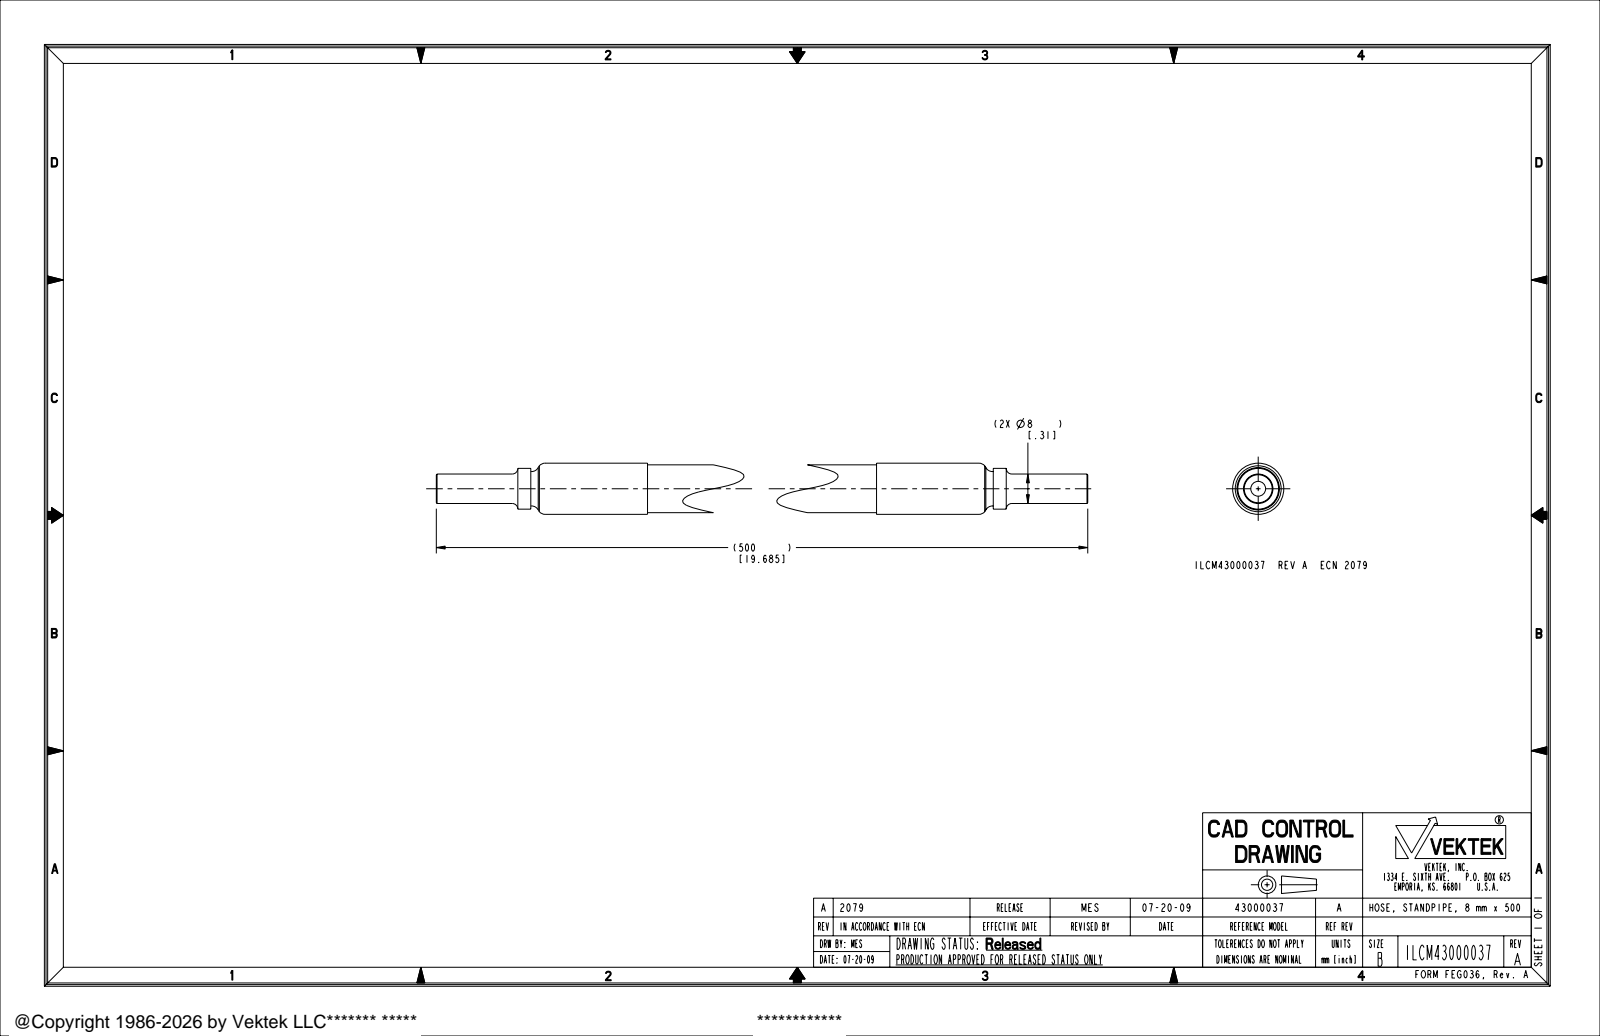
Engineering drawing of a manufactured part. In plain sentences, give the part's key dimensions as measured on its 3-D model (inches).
The part is named "ILCM43000037". Its 3-D file was written by "PRO/ENGINEER BY PARAMETRIC TECHNOLOGY CORPORATION, 2007460 (AUTOMOTIVE_DESIGN_CC2)". It is 1 solid with 74 faces: 14 planar, 28 cylindrical and 32 other. Overall it measures 19.685 by 0.543 by 0.543 inches. Its volume is 3.035 cubic inches and its surface area 51.88 square inches. Round holes: 1 of diameter 0.157, 1 of diameter 0.236, 1 of diameter 0.512. Round bosses or shafts: 1 of diameter 0.543, 1 of diameter 0.508, 1 of diameter 0.433, 1 of diameter 0.354, 1 of diameter 0.313. The main face-to-face distances are 0.073, 17.344, 17.417, 17.272, 1.134, 1.207, 18.478, 18.551, 1.004, 18.681.
